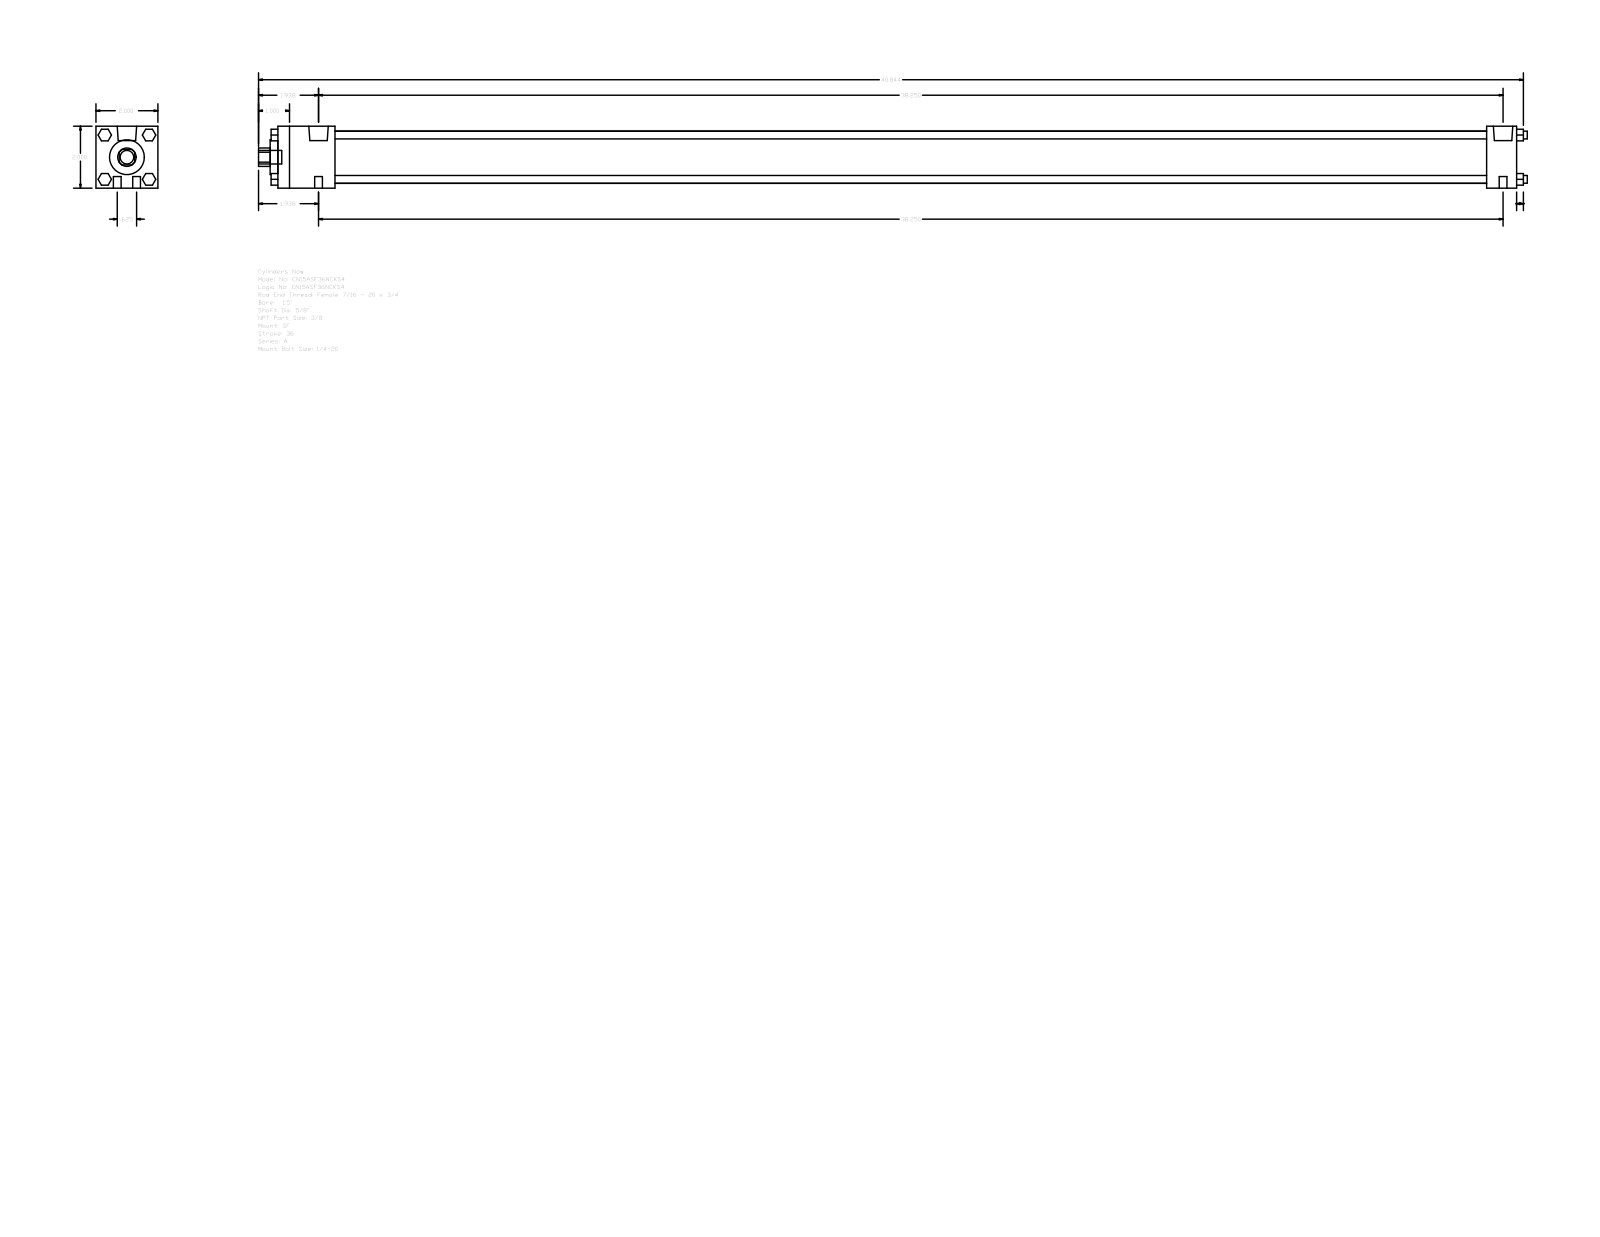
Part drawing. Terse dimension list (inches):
name: A_SF__0150_0.625
written by: GSSL Pune (CONFIG_CONTROL_DESIGN)
unit: in
bodies: 0 solids, 124 faces (94 planar, 30 cylindrical, 0 other)
size: 40.969 × 2 × 2
holes: 1× ⌀0.625, 1× ⌀1.125, 1× ⌀1.69
bosses: 8× ⌀0.25, 2× ⌀0.627, 2× ⌀0.219, 1× ⌀0.437
rounds: 1× R0.297
face distances: 2, 40, 1.844, 39.031, 37.187, 38.156, 0.969, 0.375, 0.25, 2.094
